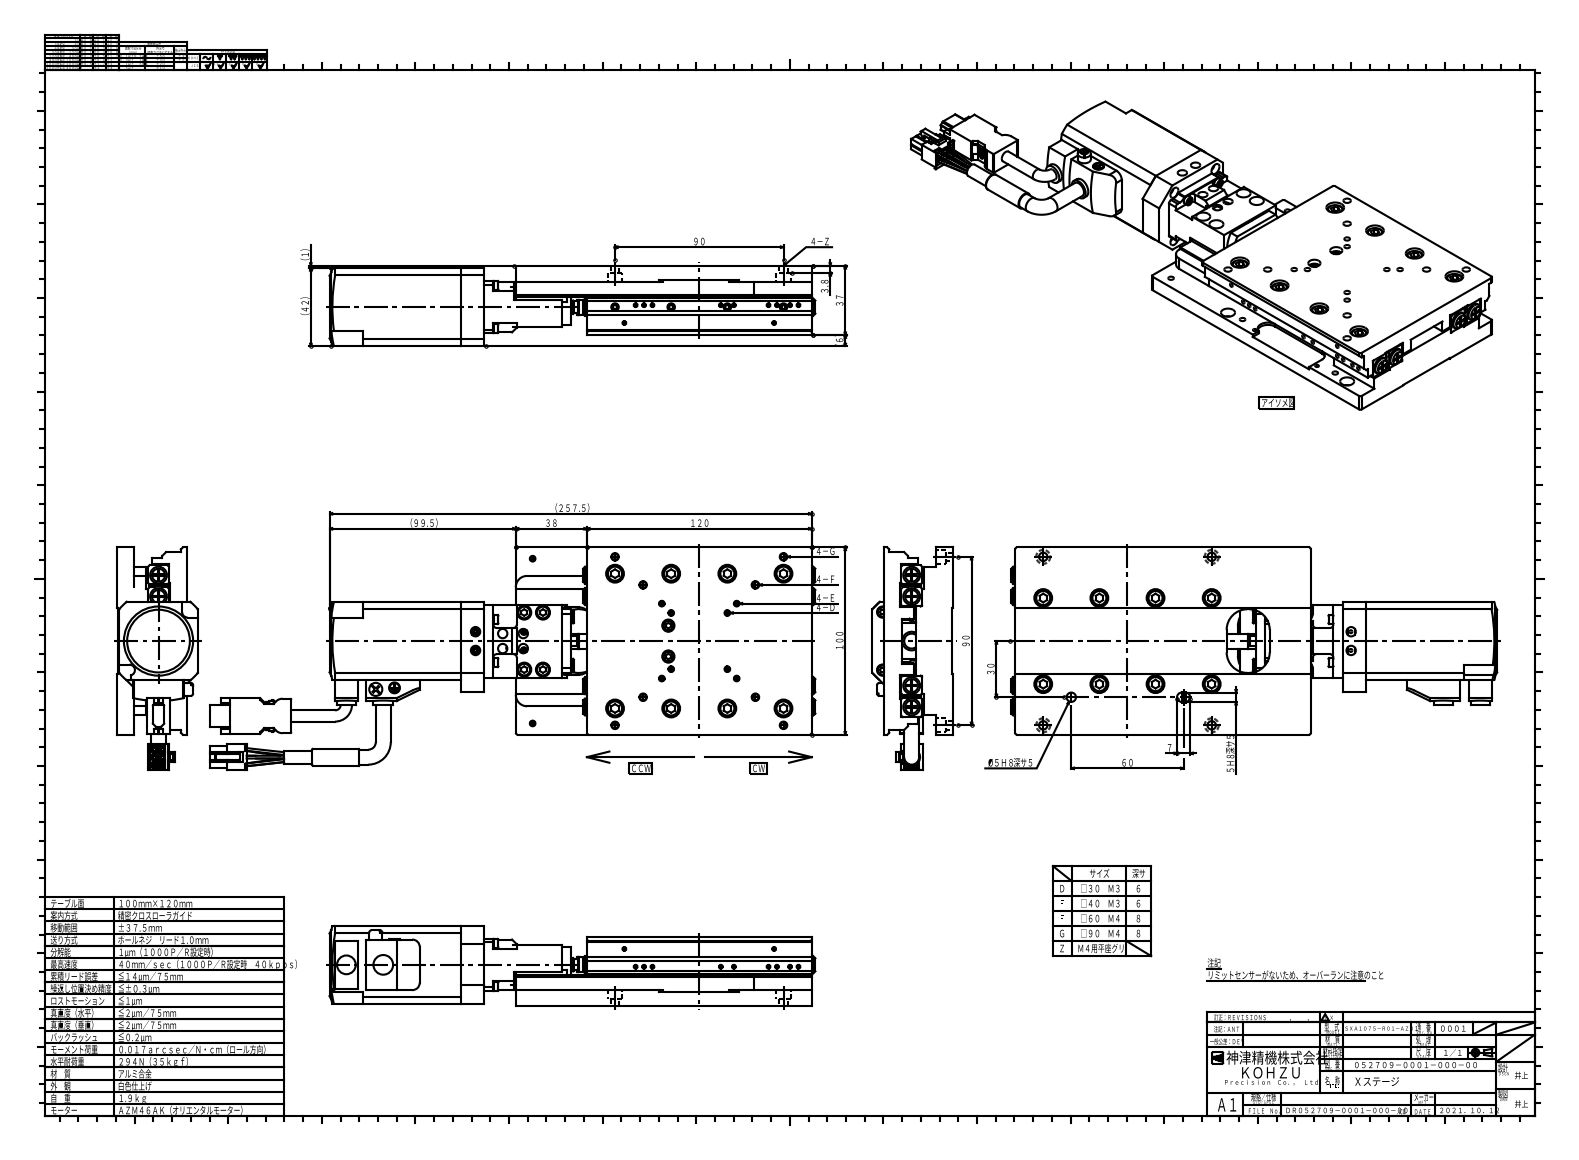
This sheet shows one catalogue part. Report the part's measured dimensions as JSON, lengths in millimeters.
{"part_name": "SXA1075-R01-AZ01-prt0; SXA1075-R01-AZ01-prt1", "step_written_by": "spGate 17.5.5 (AUTOMOTIVE_DESIGN)", "units": "millimeters", "bodies": {"solids": 2, "faces": 1264, "planar": 772, "cylindrical": 332, "other": 160}, "overall_size": [323.4, 118.9, 43], "volume_mm3": 625350, "surface_area_mm2": 114602, "round_holes": [[2, 15], [2.5, 12], [3, 12], [3.3, 8], [4, 8], [1.6, 6], [6, 6], [4.5, 4], [7.5, 4], [2.15, 2], [2.6, 2], [0.5, 1]], "round_bosses_or_shafts": [[5.5, 6], [9, 5], [7, 4], [5, 4], [4.5, 4], [8, 2], [10.5, 1], [10, 1]], "partial_cylinders_radius": [[5.5, 8], [0.25, 6], [0.3, 6], [0.5, 6], [1, 6], [4, 6], [0.4, 4], [1.5, 4]], "face_to_face_distances": [37, 9.5, 15.5, 27.5, 1, 9, 28, 26.5, 0.5, 27.2], "hole_center_spacings": [35.36, 21.21, 47.43, 50.99, 67.08, 69.64, 76.49, 30]}
